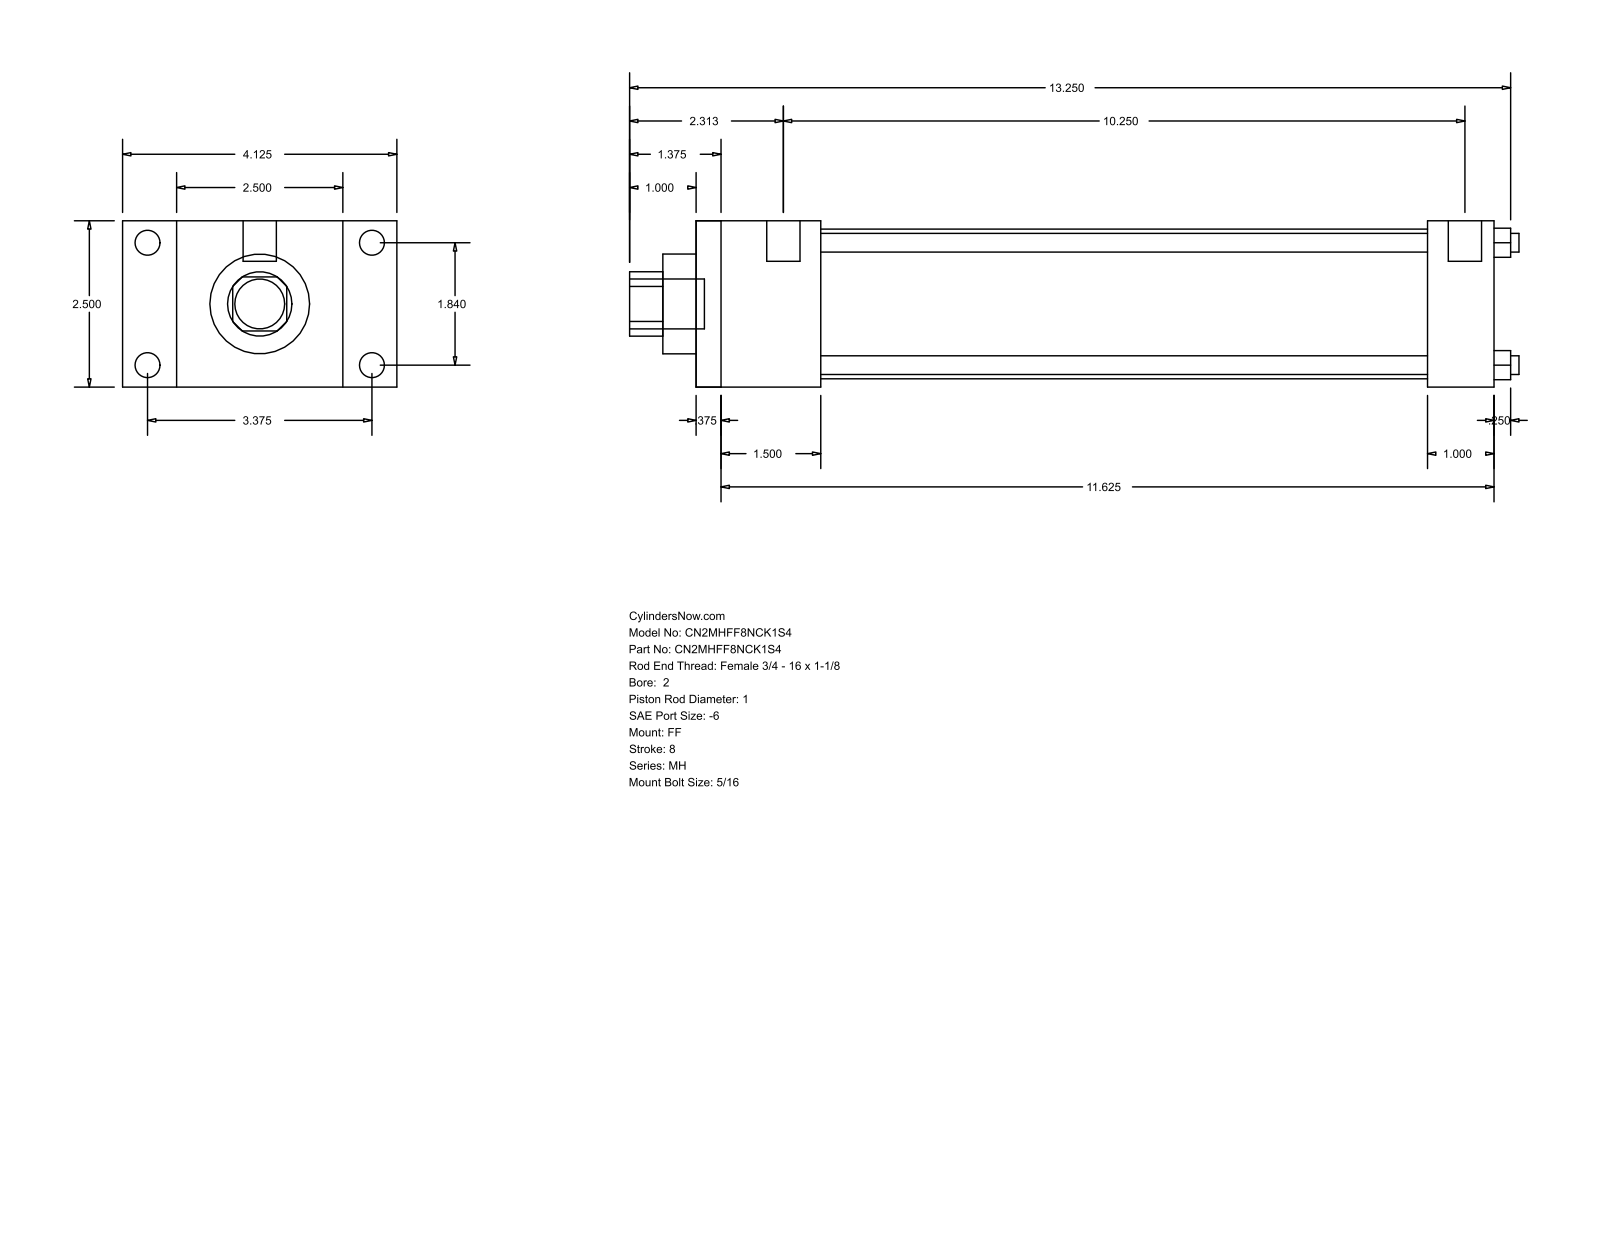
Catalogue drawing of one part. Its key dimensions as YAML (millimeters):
part_name: "MH_FF__0200_1"
step_written_by: "GSSL Pune (CONFIG_CONTROL_DESIGN)"
units: millimeters
bodies: {solids: 0, faces: 92, planar: 64, cylindrical: 28, other: 0}
overall_size: [339.73, 104.78, 63.5]
round_holes:
  - {diameter: 7.14, count: 4}
  - {diameter: 25.4, count: 1}
  - {diameter: 38.1, count: 1}
  - {diameter: 57.15, count: 1}
round_bosses_or_shafts:
  - {diameter: 9.53, count: 4}
  - {diameter: 5.56, count: 4}
  - {diameter: 12.7, count: 2}
  - {diameter: 19.05, count: 1}
partial_cylinders:
  - {radius: 12.29, count: 1}
face_to_face_distances: [63.5, 304.8, 9.52, 295.28, 20.64, 25.4, 47.63, 279.4, 38.11, 269.88]
hole_center_spacings: [33.05, 46.74, 66.1]
